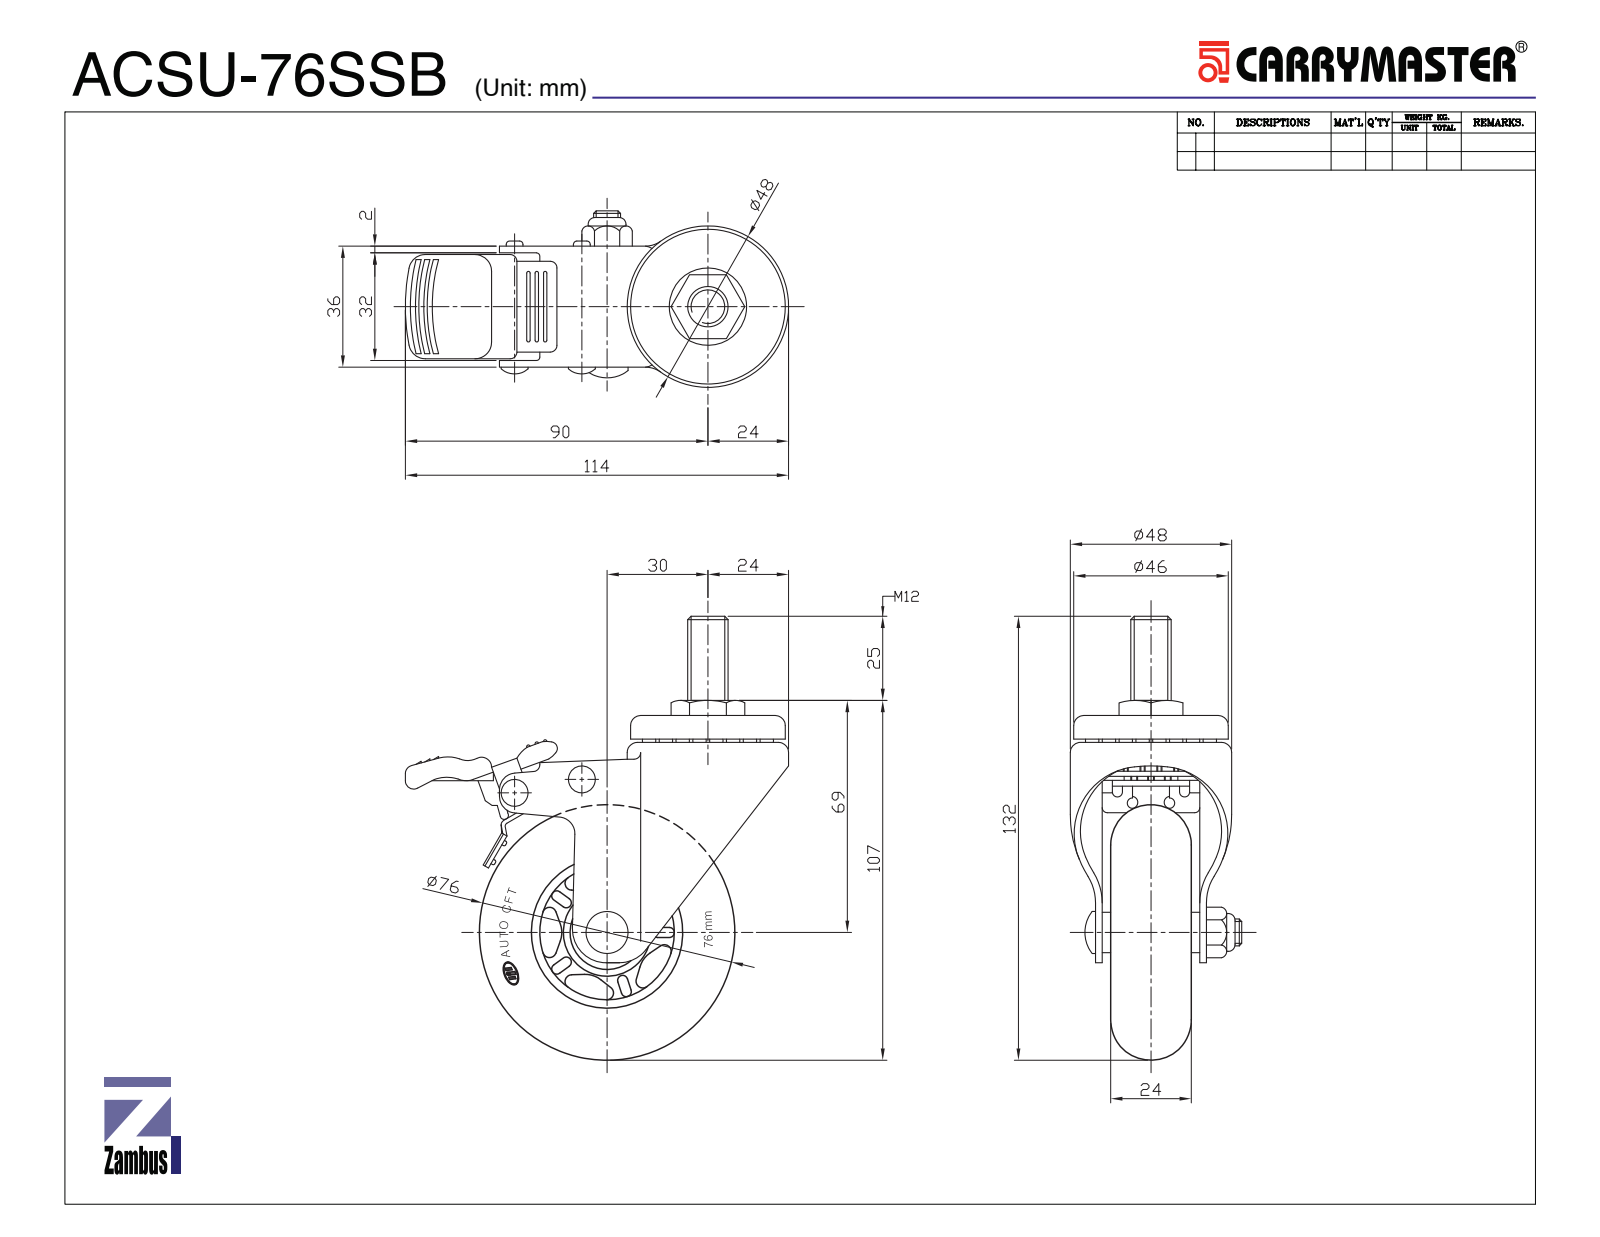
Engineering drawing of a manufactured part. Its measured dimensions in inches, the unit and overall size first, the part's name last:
Units: inches
Overall size (bounding box): 5.233 × 4.479 × 1.929
Round holes (diameter × count): ⌀0.138 ×2, ⌀0.157 ×2, ⌀0.268 ×1, ⌀0.315 ×1, ⌀0.319 ×1, ⌀0.433 ×1, ⌀0.682 ×1, ⌀0.728 ×1, ⌀0.866 ×1, ⌀1.063 ×1, ⌀1.543 ×1, ⌀1.713 ×1
Round bosses / shafts (diameter × count): ⌀0.193 ×2, ⌀1.87 ×1, ⌀1.669 ×1, ⌀1.193 ×1, ⌀0.709 ×1, ⌀0.63 ×1, ⌀0.499 ×1, ⌀0.492 ×1
Partial cylindrical surfaces — rounded edges, fillets, slot ends (radius × count): R0.039 ×53, R0.03 ×44, R0.059 ×28, R0.049 ×26, R0.02 ×22, R0.079 ×12, R0.118 ×9, R0.098 ×7
Main face-to-face distances: 0.079, 1.398, 0.138, 0.059, 0.266, 1.211, 0.187, 1.132, 1.319, 1.476
Hole centre spacings: 0.824, 1.77, 1.91
Volume: 8.367 in³ · Surface area: 125.4 in²
Bodies: 20 solids, 1099 faces (398 planar, 458 cylindrical, 243 other)
Part name (STEP PRODUCT): ACSU-76SSB
STEP written by: SolidWorks 2015 (CONFIG_CONTROL_DESIGN)
